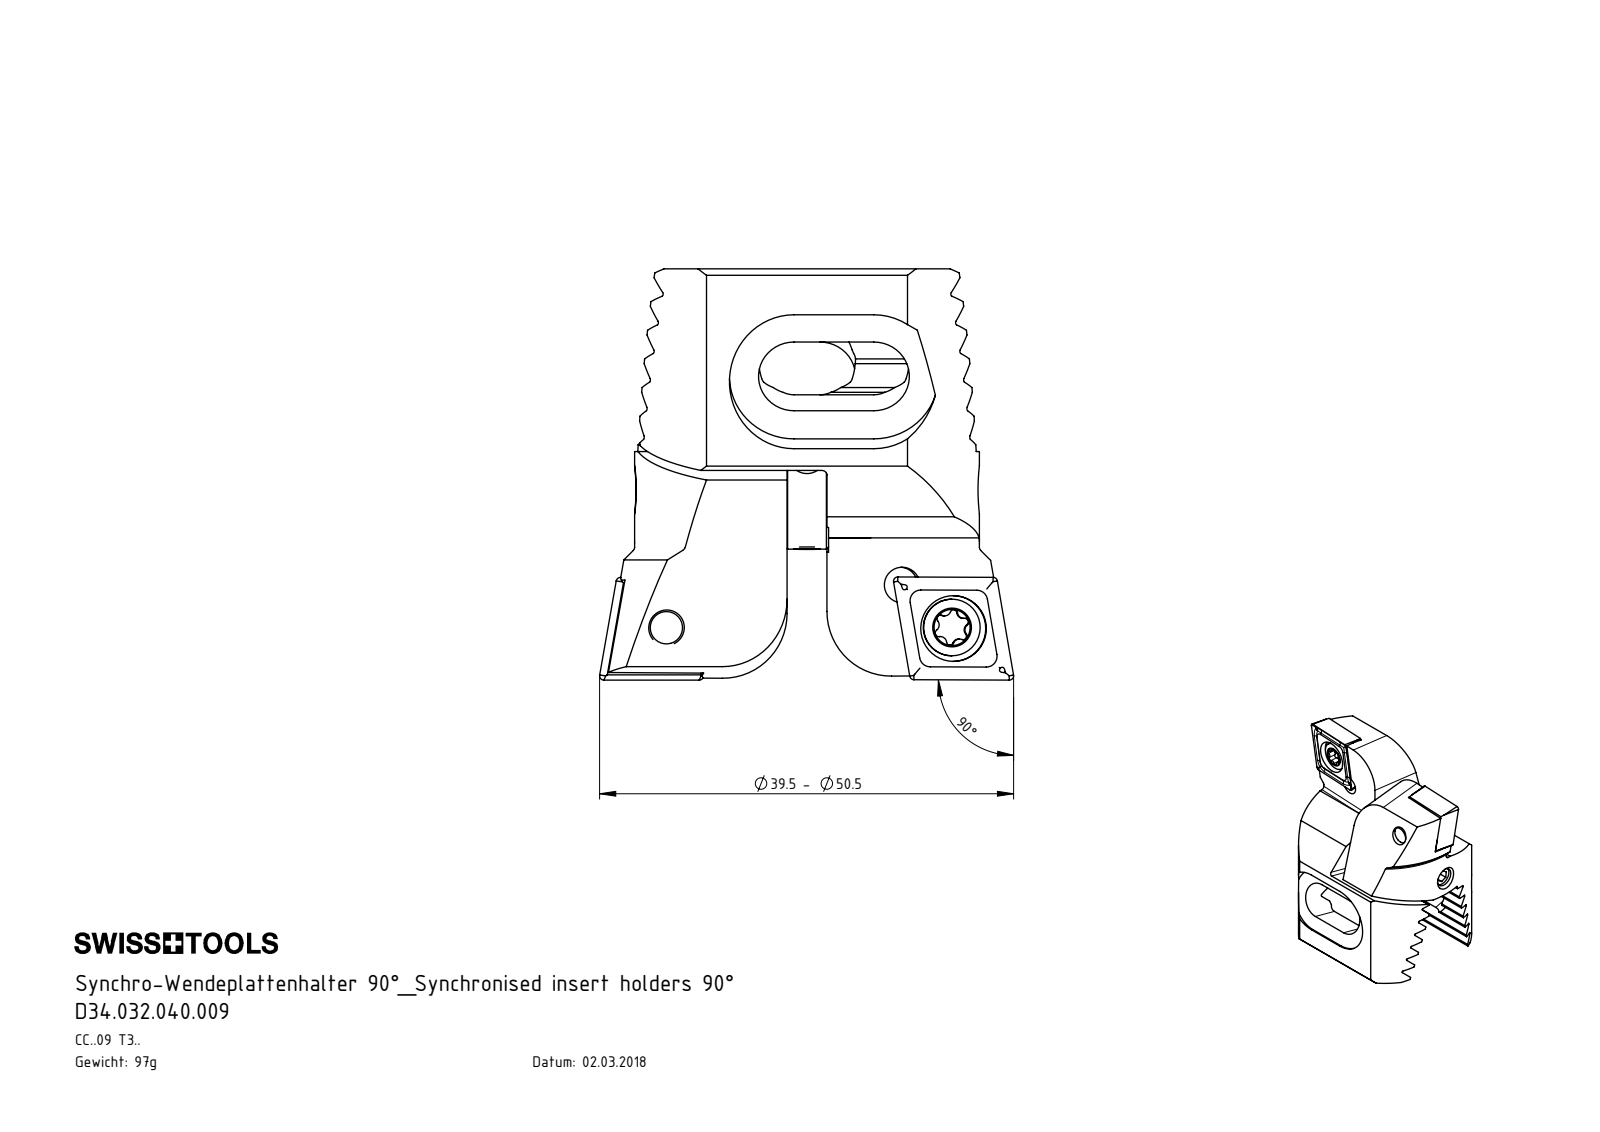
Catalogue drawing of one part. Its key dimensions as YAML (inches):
part_name: "D34.032.040.009; Z25-ER3.002.004_B; Z32-ER3.001.030_A; WCB-ER2.001.009_A (+4 more)"
step_written_by: "SolidWorks 2017 (CONFIG_CONTROL_DESIGN)"
units: inches
bodies: {solids: 11, faces: 503, planar: 193, cylindrical: 158, other: 152}
overall_size: [1.513, 1.502, 1.031]
volume: 0.754
surface_area: 13.74
round_holes:
  - {diameter: 0.13, count: 4}
  - {diameter: 0.039, count: 3}
  - {diameter: 0.098, count: 3}
  - {diameter: 0.173, count: 2}
  - {diameter: 0.24, count: 2}
  - {diameter: 0.138, count: 1}
round_bosses_or_shafts:
  - {diameter: 0.118, count: 4}
  - {diameter: 0.157, count: 3}
  - {diameter: 0.207, count: 2}
  - {diameter: 0.433, count: 1}
partial_cylinders:
  - {radius: 0.008, count: 12}
  - {radius: 0.013, count: 12}
  - {radius: 0.023, count: 12}
  - {radius: 0.039, count: 8}
  - {radius: 0.236, count: 6}
  - {radius: 0.02, count: 4}
  - {radius: 0.13, count: 4}
  - {radius: 0.63, count: 2}
face_to_face_distances: [0.094, 0.375, 0.281, 0.187, 0.469, 0.152, 0.188, 0.032, 0.161, 0.379]
hole_center_spacings: [0.394, 1.066, 0.079, 0.24, 0.24, 0.246, 0.246, 0.402]
